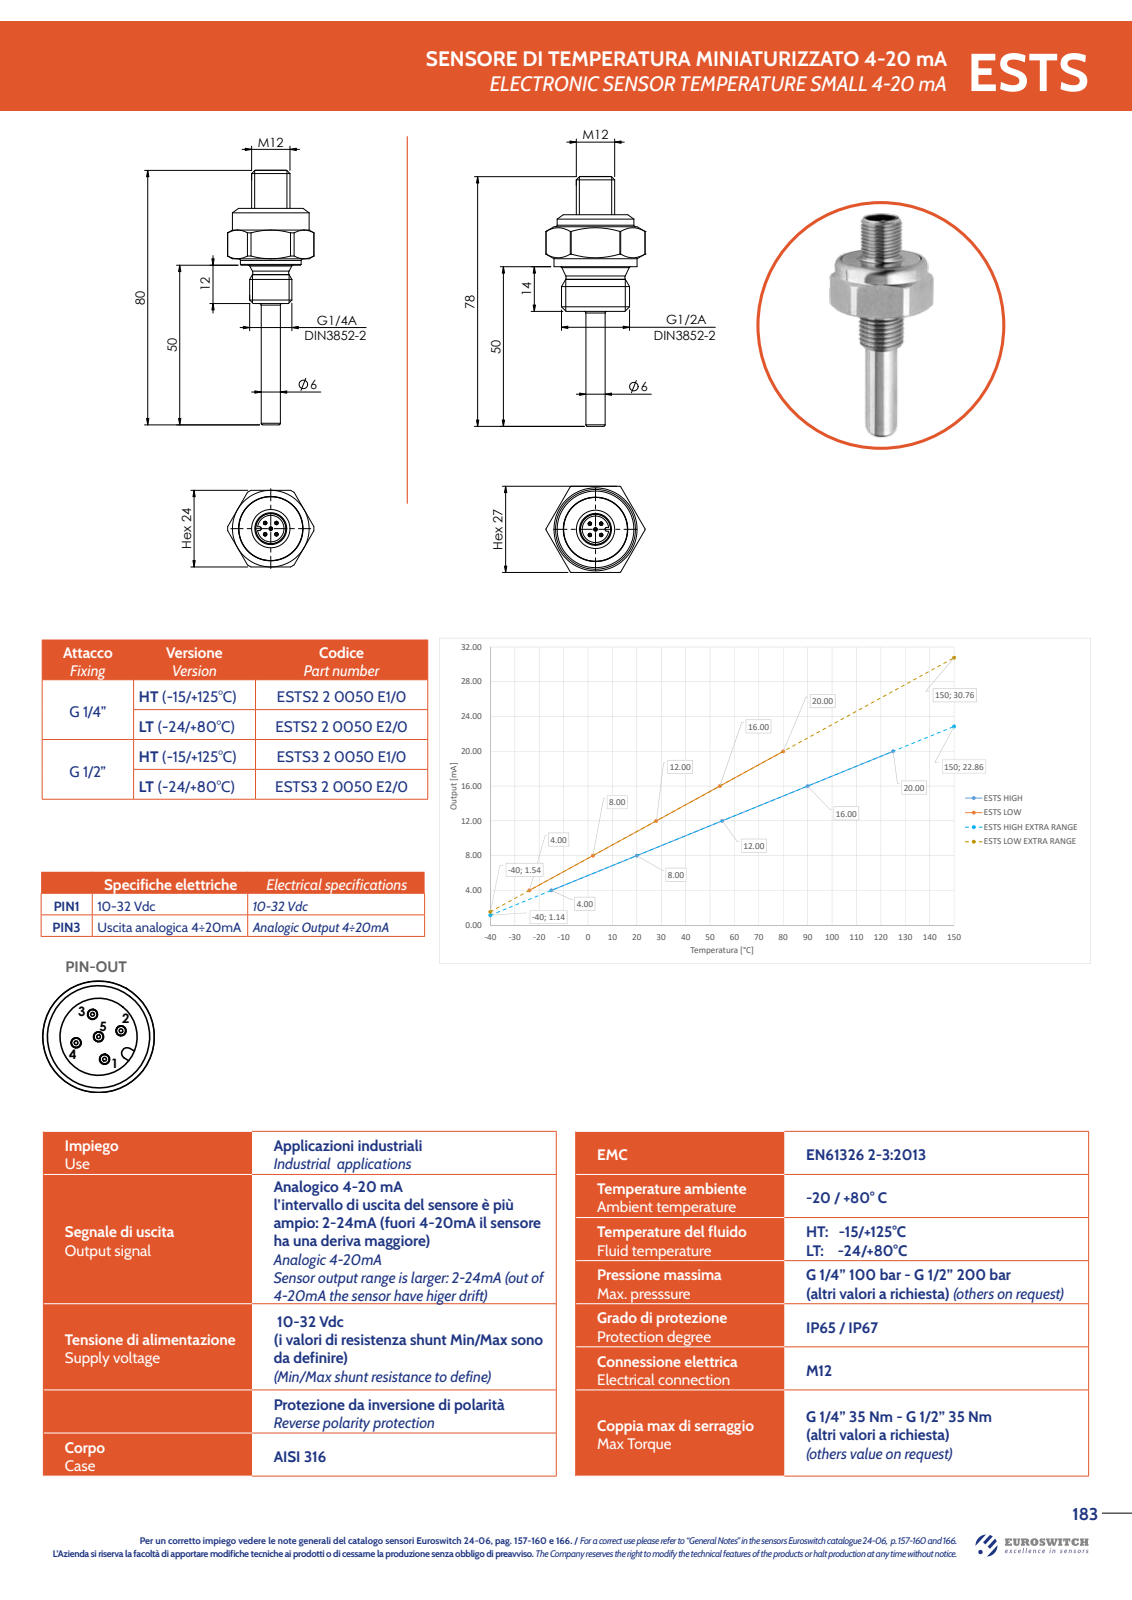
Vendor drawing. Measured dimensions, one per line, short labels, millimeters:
name: ESTS
written by: SolidWorks 2019 (AUTOMOTIVE_DESIGN)
unit: mm
bodies: 0 solids, 90 faces (19 planar, 33 cylindrical, 38 other)
size: 80 × 31 × 27
holes: 1× ⌀8.3
bosses: 5× ⌀1, 1× ⌀26, 1× ⌀24, 1× ⌀21.3, 1× ⌀12, 1× ⌀9.45, 1× ⌀6
rounds: 1× R0.6, 1× R15.5
face distances: 27, 31.9, 14, 17.9, 26.5, 12.5, 5.4, 36, 50, 62.5
